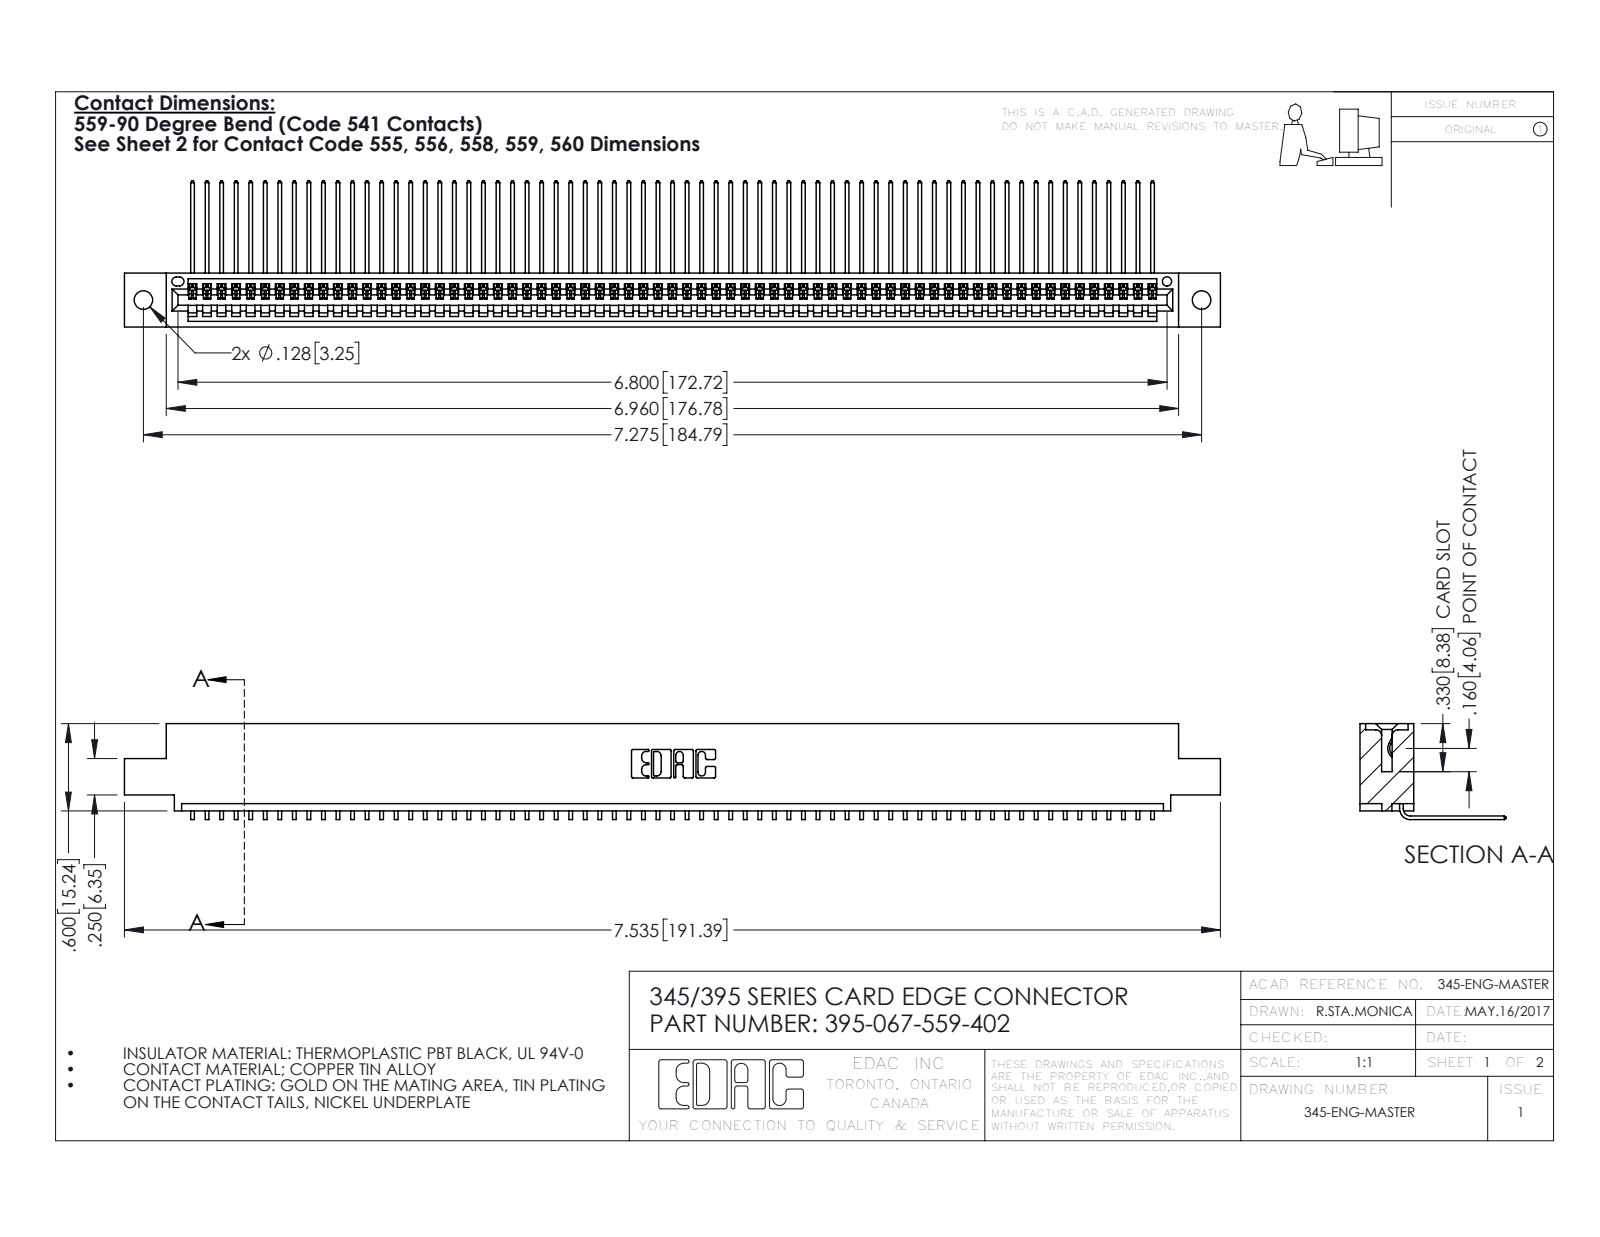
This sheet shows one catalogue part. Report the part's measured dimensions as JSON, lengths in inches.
{"part_name": "345 Part_0.110 Offset - 0.128 Dia; 395-067-559-402; 345-292-001_558 559 Tail - 1", "step_written_by": "SolidWorks 2016 (CONFIG_CONTROL_DESIGN)", "units": "inches", "bodies": {"solids": 68, "faces": 4150, "planar": 2898, "cylindrical": 1252, "other": 0}, "overall_size": [7.535, 1.005, 0.659], "volume_in3": 1.129, "surface_area_in2": 40.36, "round_holes": [[0.128, 2], [0.064, 1]], "partial_cylinders_radius": [[0.006, 134], [0.01, 22], [0.007, 6], [0.031, 6], [0.026, 3], [0.031, 2], [0.04, 2], [0.014, 1]], "face_to_face_distances": [0.072, 0.298, 0.37, 0.2, 0.098, 0.272, 0.025, 0.225, 0.149, 0.072], "hole_center_spacings": [0.27, 7.039, 7.275]}
